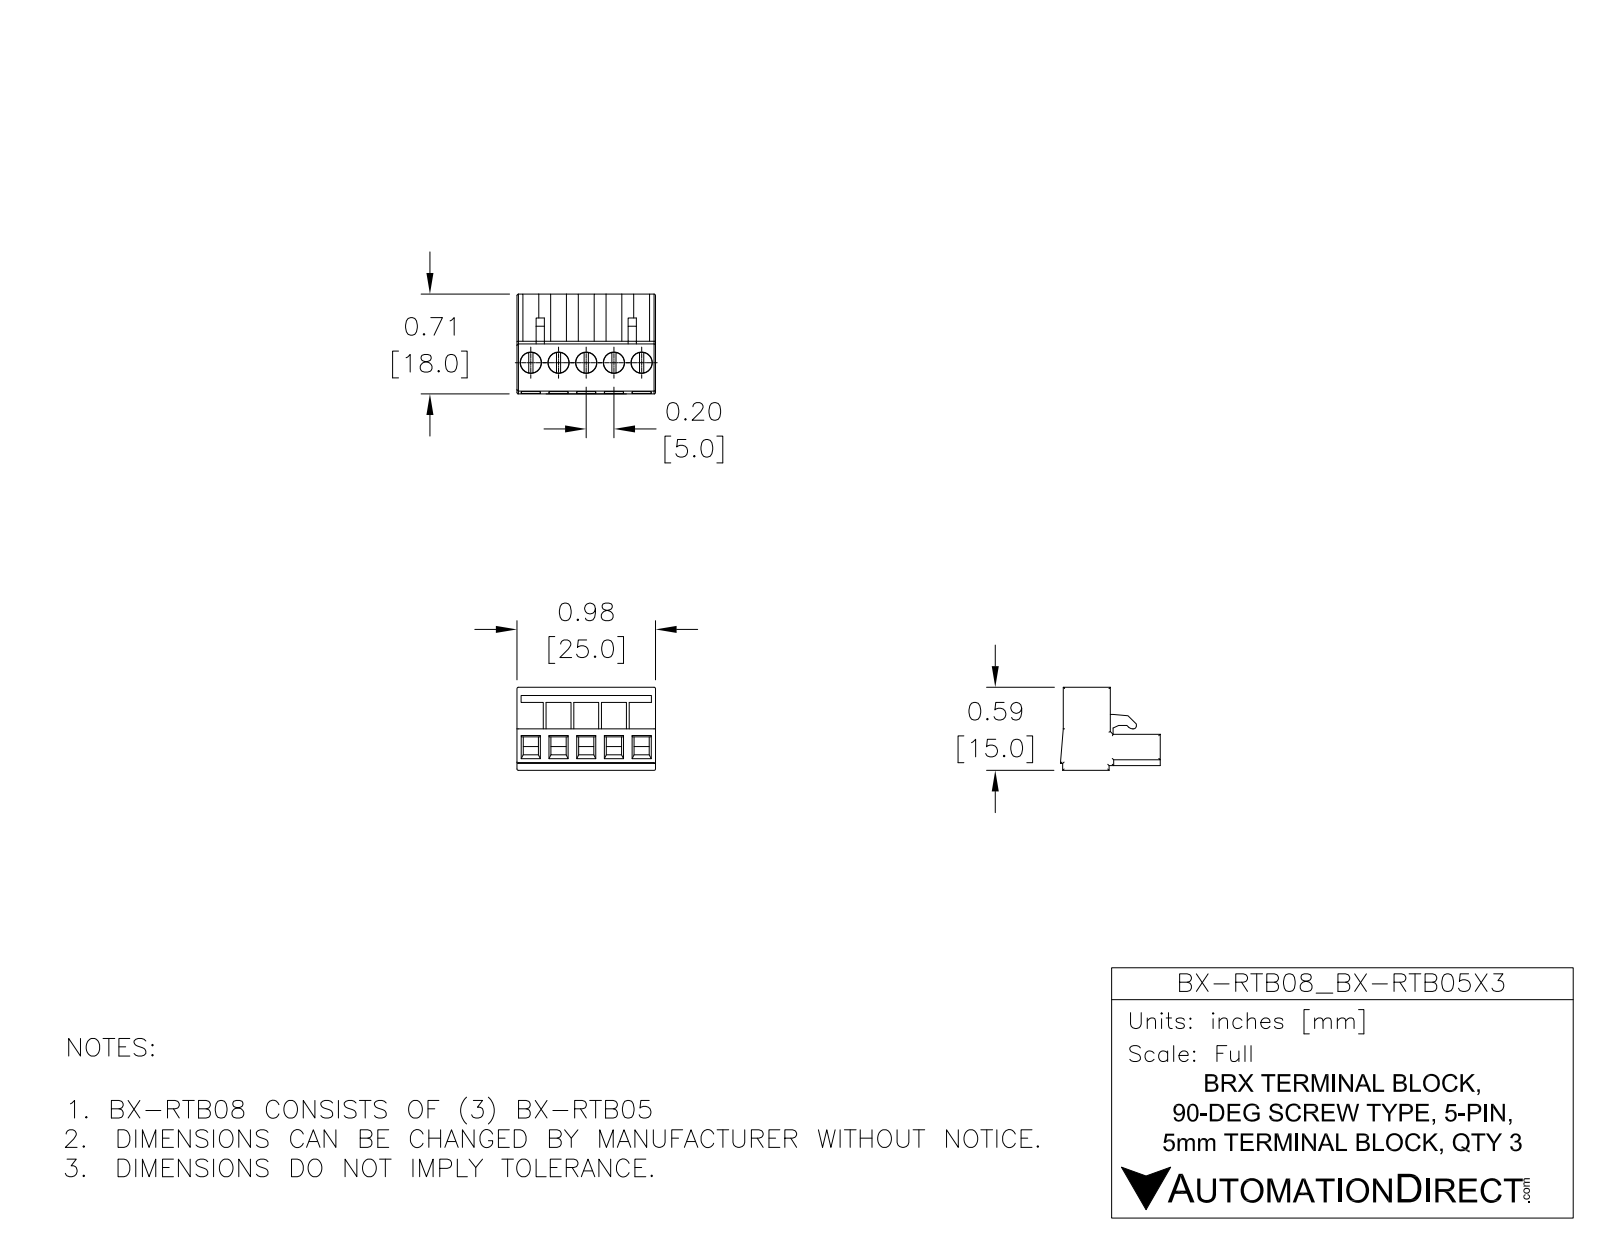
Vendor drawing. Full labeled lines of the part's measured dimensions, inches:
Part name (STEP PRODUCT): BX-RTB08
STEP written by: SolidWorks 2017 (AUTOMOTIVE_DESIGN)
Units: inches
Bodies: 3 solids, 870 faces (594 planar, 246 cylindrical, 30 other)
Overall size (bounding box): 3.953 × 0.709 × 0.591
Volume: 0.699 in³ · Surface area: 14.2 in²
Round holes (diameter × count): ⌀0.063 ×15, ⌀0.124 ×15, ⌀0.152 ×15
Round bosses / shafts (diameter × count): ⌀0.148 ×15
Partial cylindrical surfaces — rounded edges, fillets, slot ends (radius × count): R0.01 ×85, R0.099 ×15, R0.02 ×1, R0.039 ×1
Main face-to-face distances: 0.335, 1.484, 0.984, 0.591, 0.224, 0.366, 0.256, 2.969, 2.469, 0.5
Hole centre spacings: 0.197, 1.484, 0.394, 1.287, 1.681, 0.591, 1.091, 1.878
